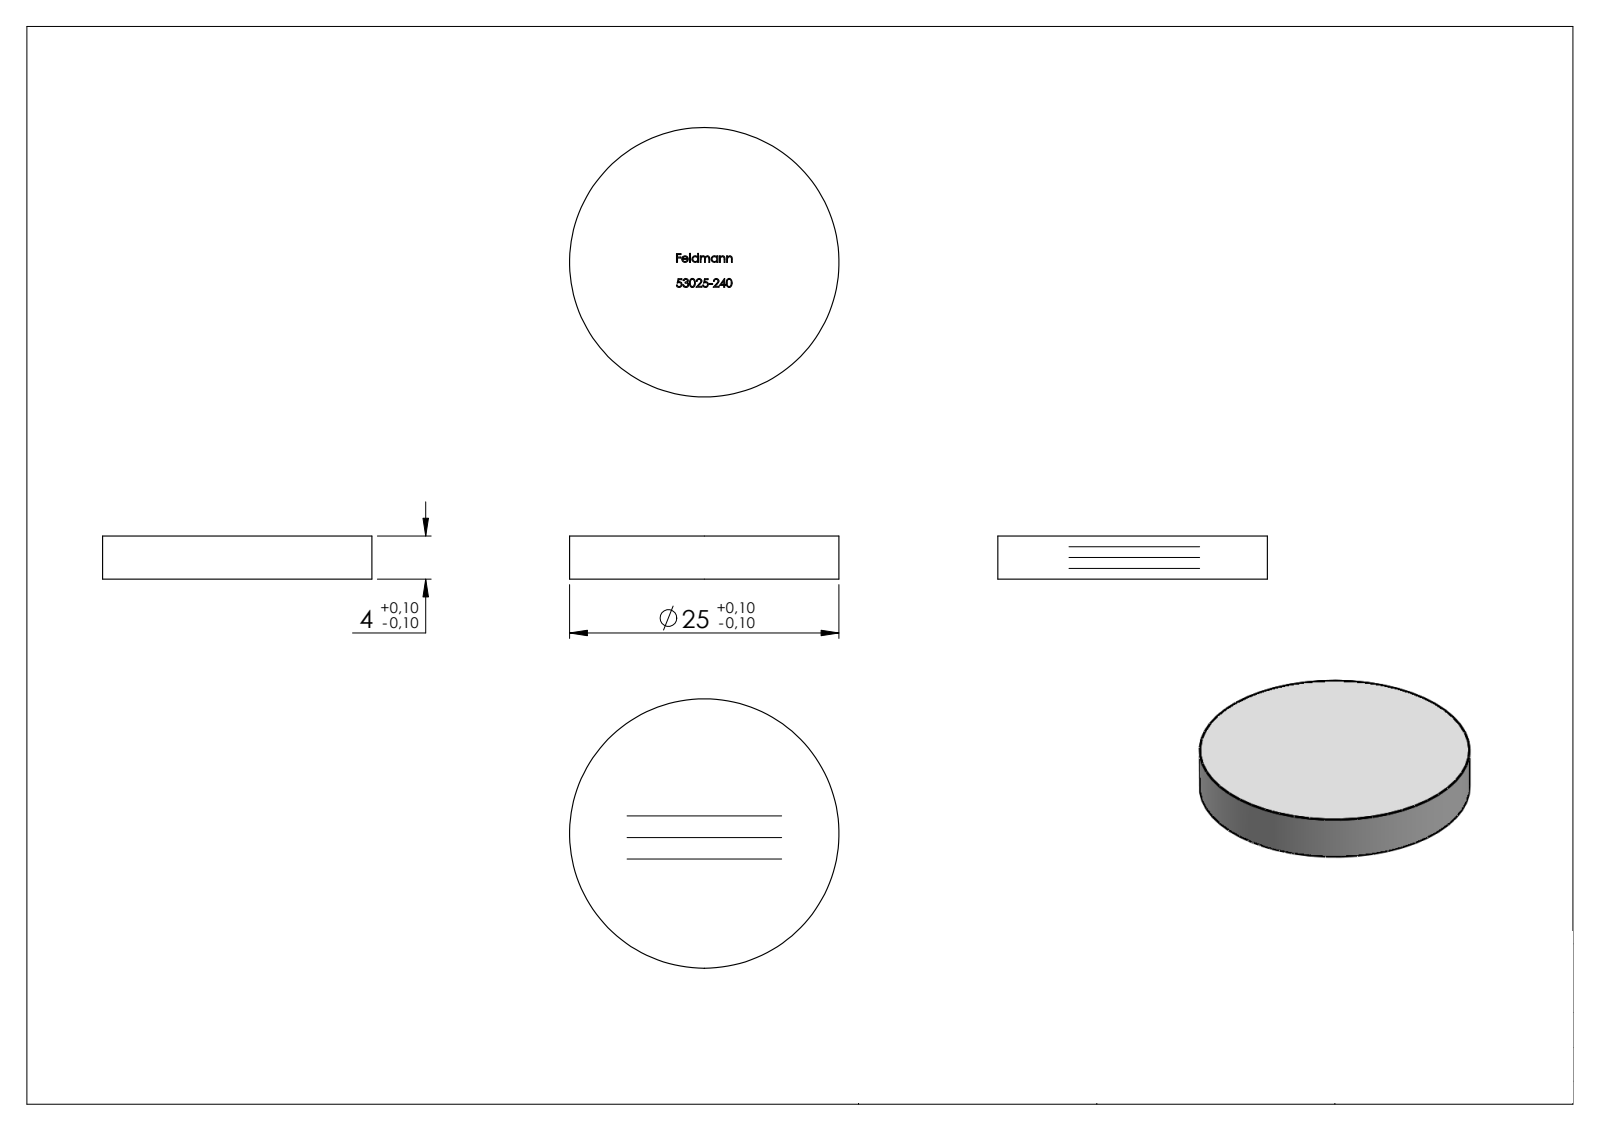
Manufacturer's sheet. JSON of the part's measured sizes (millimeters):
{"part_name": "53025-240", "step_written_by": "SolidWorks 2018 (CONFIG_CONTROL_DESIGN)", "units": "millimeters", "bodies": {"solids": 1, "faces": 233, "planar": 123, "cylindrical": 2, "other": 108}, "overall_size": [25, 25, 4], "volume_mm3": 1963, "surface_area_mm2": 1302, "round_bosses_or_shafts": [[25, 1]], "face_to_face_distances": [4, 3.9, 1.78, 2.45, 0.71, 0.83, 0.79, 2.41, 0.99, 0.4]}
